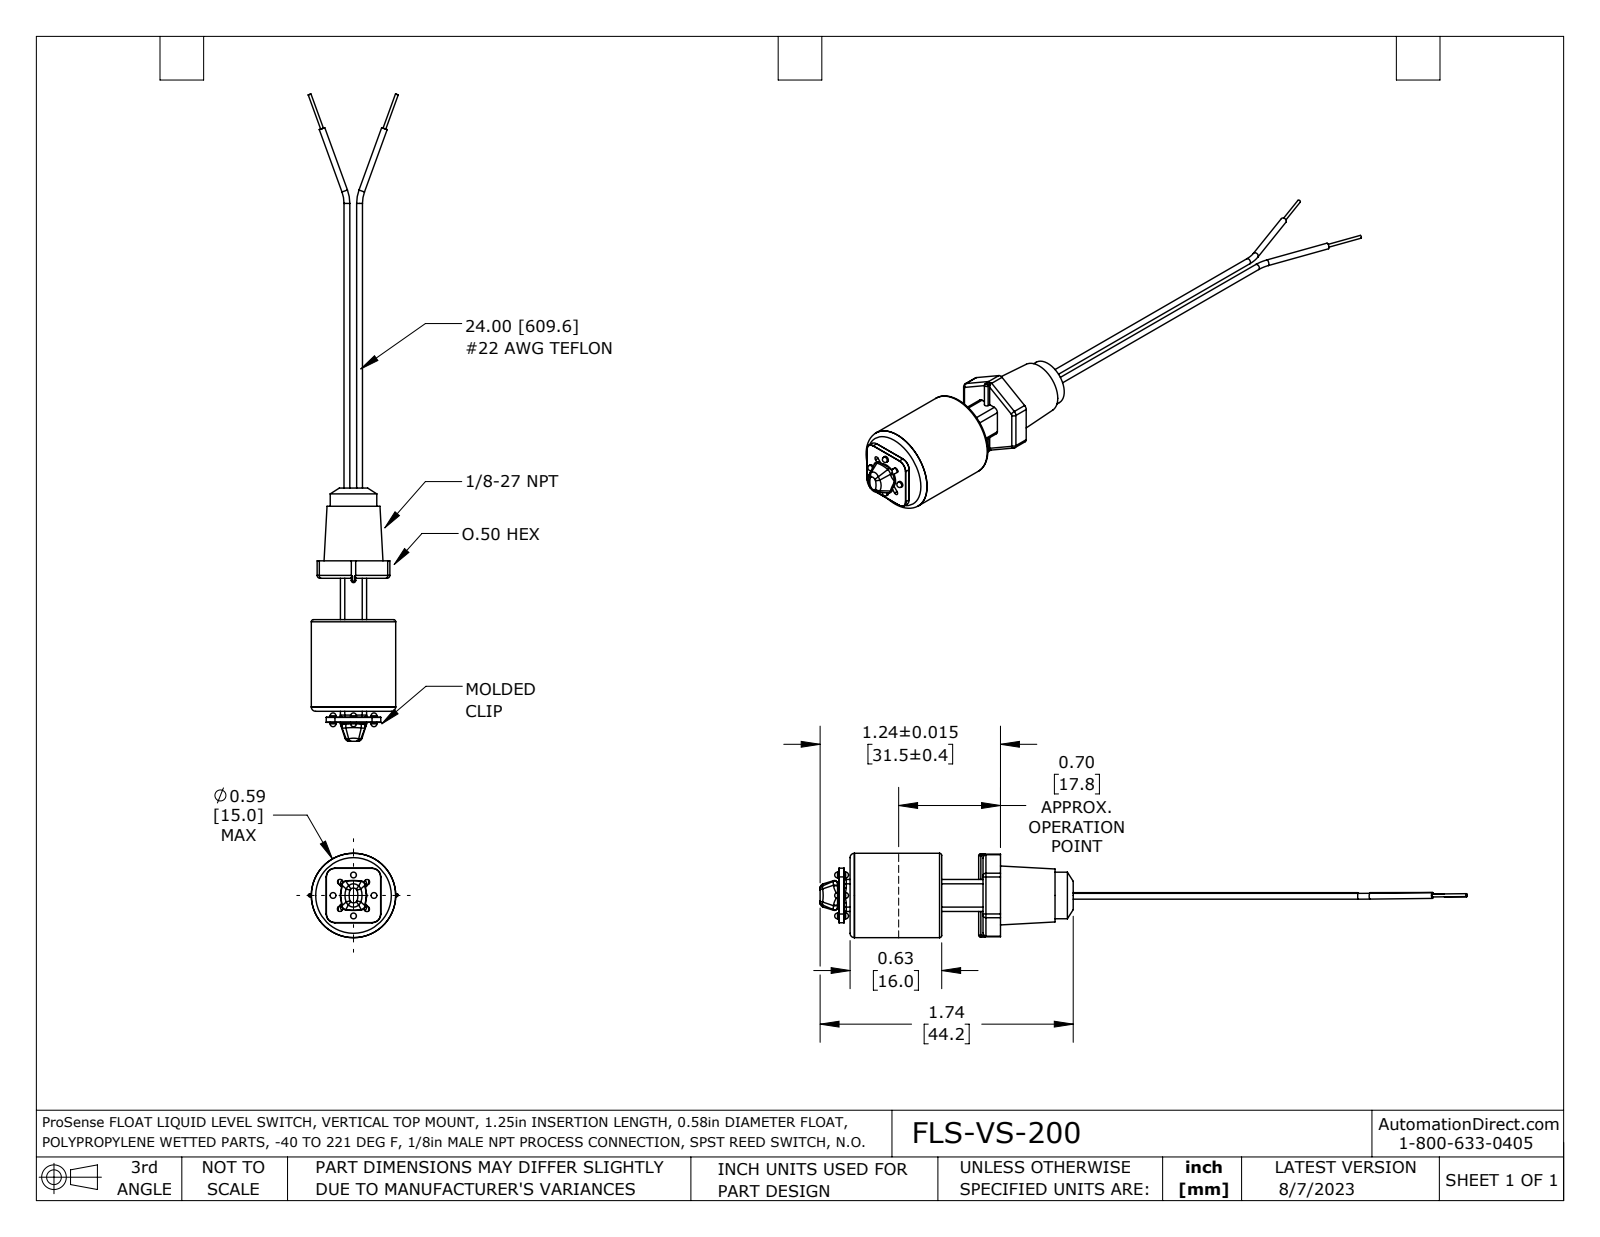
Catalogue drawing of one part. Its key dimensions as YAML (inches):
part_name: "ADM3326-NPT-NO nc fxt"
step_written_by: "SolidWorks 2021 (AUTOMOTIVE_DESIGN)"
units: inches
bodies: {solids: 9, faces: 387, planar: 127, cylindrical: 149, other: 111}
overall_size: [4.448, 0.619, 0.58]
volume: 0.201
surface_area: 9.574
round_holes:
  - {diameter: 0.068, count: 2}
  - {diameter: 0.035, count: 1}
  - {diameter: 0.039, count: 1}
  - {diameter: 0.18, count: 1}
  - {diameter: 0.185, count: 1}
  - {diameter: 0.498, count: 1}
  - {diameter: 0.5, count: 1}
  - {diameter: 0.558, count: 1}
round_bosses_or_shafts:
  - {diameter: 0.04, count: 8}
  - {diameter: 0.063, count: 2}
  - {diameter: 0.05, count: 2}
  - {diameter: 0.02, count: 2}
  - {diameter: 0.58, count: 1}
  - {diameter: 0.52, count: 1}
  - {diameter: 0.32, count: 1}
  - {diameter: 0.178, count: 1}
partial_cylinders:
  - {radius: 0.01, count: 15}
  - {radius: 0.03, count: 10}
  - {radius: 0.015, count: 9}
  - {radius: 0.02, count: 6}
  - {radius: 0.017, count: 4}
  - {radius: 0.025, count: 4}
  - {radius: 0.045, count: 4}
  - {radius: 0.055, count: 4}
face_to_face_distances: [0.03, 0.25, 0.015, 0.195, 0.04, 0.055, 0.235, 0.093, 0.197, 0.053]
hole_center_spacings: [0.202, 0.042, 0.045, 0.087, 0.201, 0.206, 0.208, 0.212]
